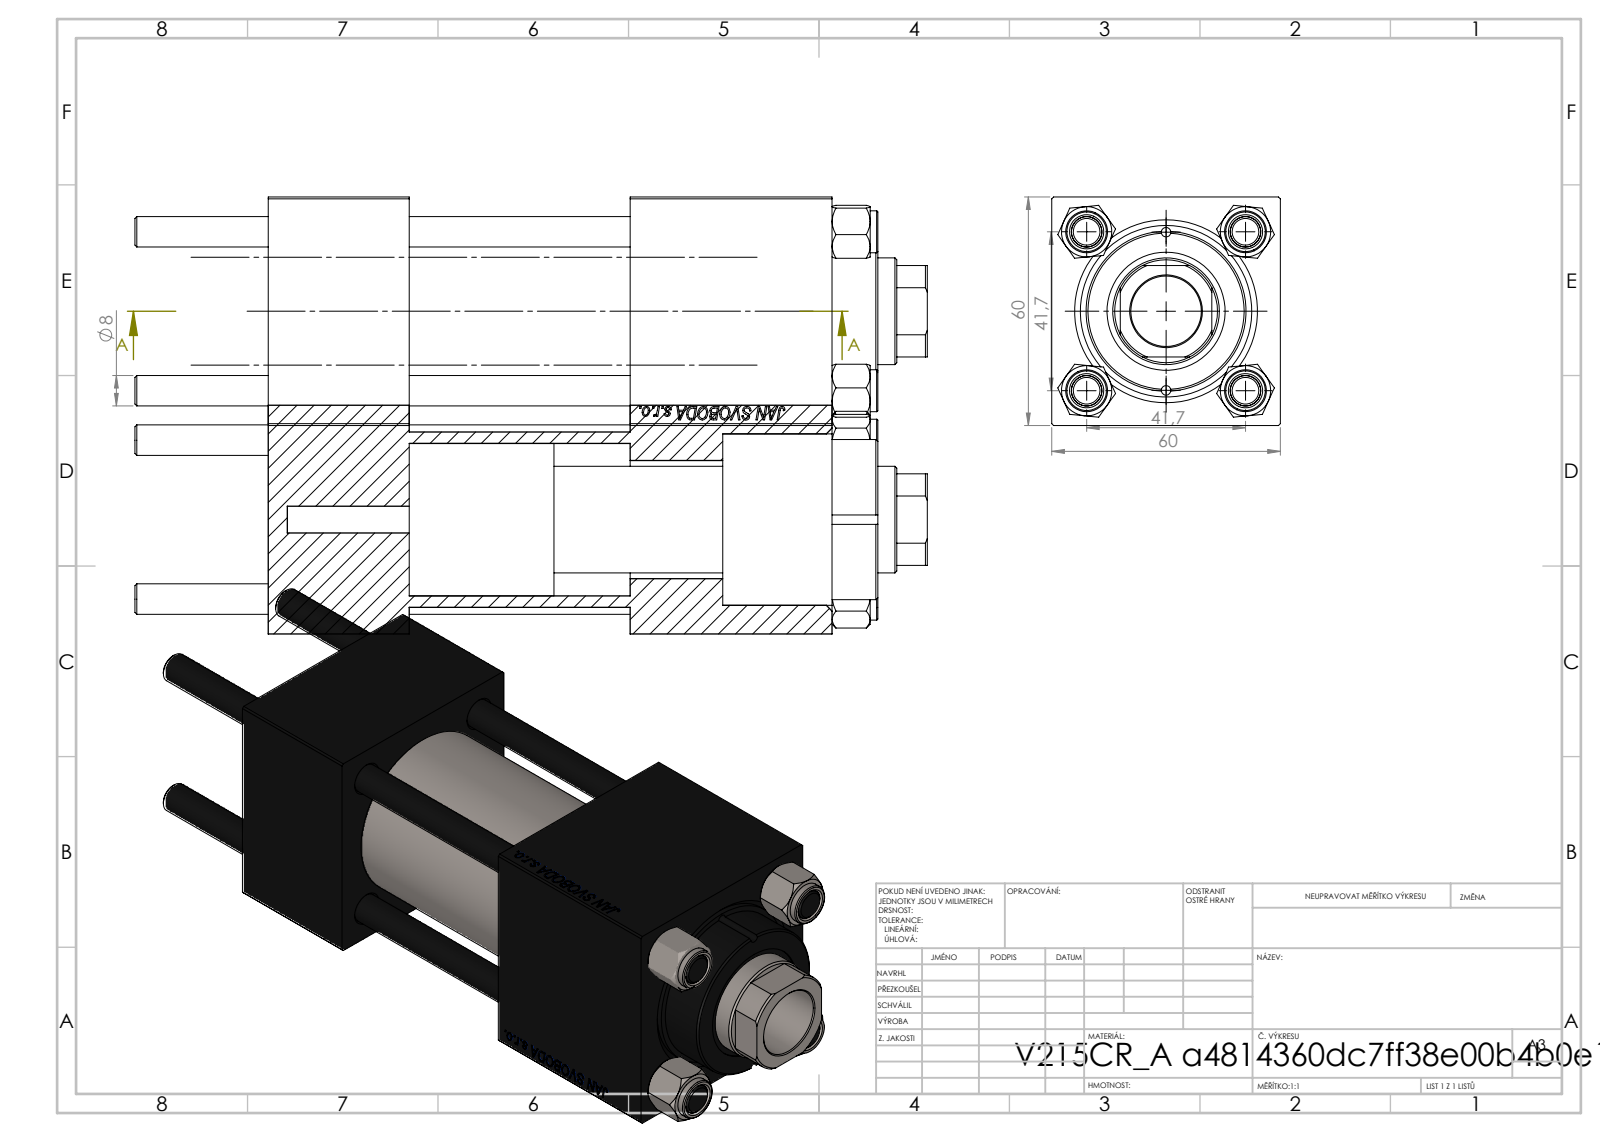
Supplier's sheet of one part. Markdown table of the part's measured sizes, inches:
| quantity | value |
| --- | --- |
| part name | V215_VC_A; V215CR_BODY_A; NUT_M5; V215CR_VCP (+1 more) |
| STEP written by | SolidWorks 2019 (CONFIG_CONTROL_DESIGN) |
| units | inches |
| bodies | 11 solids, 1141 faces (523 planar, 82 cylindrical, 536 other) |
| overall size | 8.189 × 2.362 × 2.362 |
| volume | 26.57 in³ |
| surface area | 186.4 in² |
| round holes (diameter × count) | 0.315 × 4, 0.098 × 2, 0.276 × 2, 0.656 × 2, 0.945 × 2, 0.728 × 1, 1.102 × 1, 1.22 × 1, 1.575 × 1, 1.772 × 1 |
| round bosses / shafts (diameter × count) | 0.433 × 4, 1.811 × 1, 1.654 × 1 |
| partial cylindrical surfaces (radius × count) | 0.531 × 1 |
| main face-to-face distances | 2.362, 1.457, 2.283, 3.74, 2.087, 5.827, 4.37, 4.697, 3.24, 0.957 |
| hole center spacings | 0.821, 1.161, 1.642, 1.832, 0.817, 2.322, 1.634, 3.642 |
